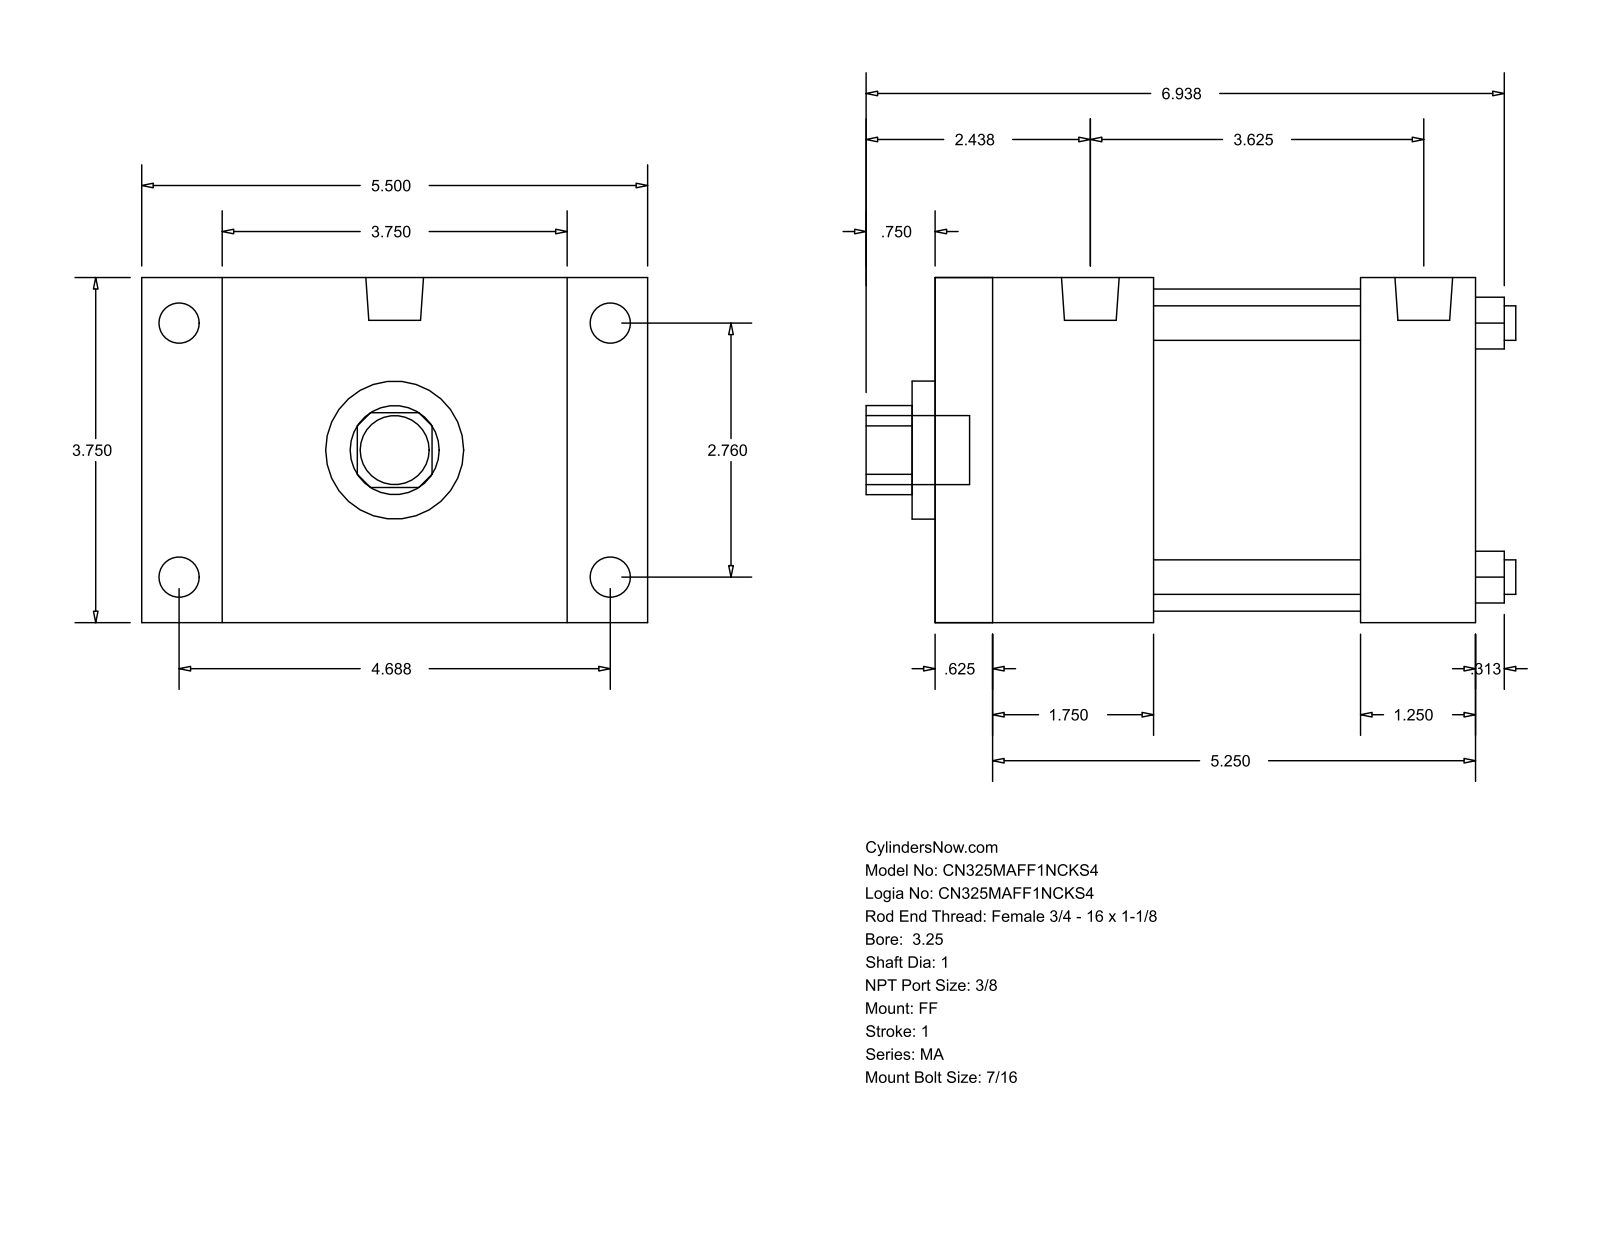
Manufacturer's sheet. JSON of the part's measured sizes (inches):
{"part_name": "MA_FF__0325_1", "step_written_by": "GSSL Pune (CONFIG_CONTROL_DESIGN)", "units": "inches", "bodies": {"solids": 0, "faces": 92, "planar": 64, "cylindrical": 28, "other": 0}, "overall_size": [7.063, 5.5, 3.75], "round_holes": [[0.375, 4], [1, 1], [1.5, 1], [3.5, 1]], "round_bosses_or_shafts": [[0.437, 8], [0.627, 2], [0.75, 1]], "partial_cylinders_radius": [[0.484, 1]], "face_to_face_distances": [3.75, 5.875, 0.625, 5.25, 0.875, 4.625, 2.375, 4.625, 1.75, 4], "hole_center_spacings": [1.952, 2.76, 3.903]}
